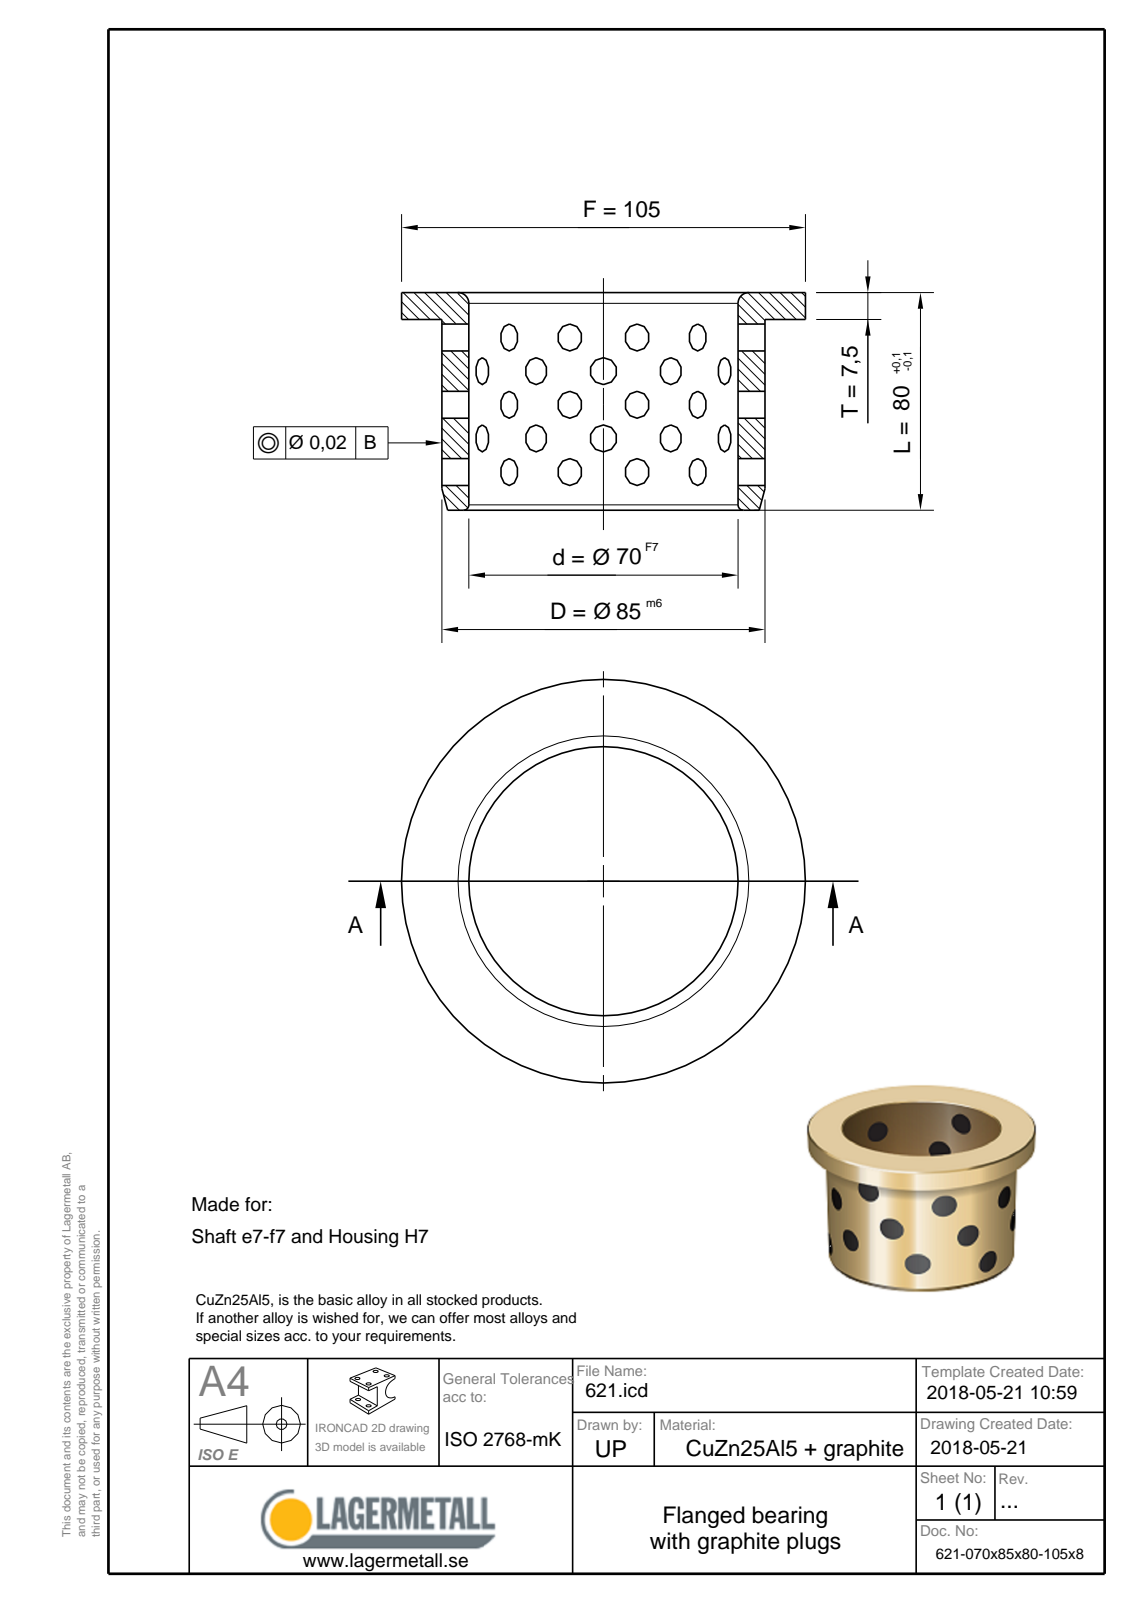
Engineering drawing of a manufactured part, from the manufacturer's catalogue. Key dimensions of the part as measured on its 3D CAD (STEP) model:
Part name (STEP PRODUCT): 621-070x85x80-105x8
STEP written by: Spatial InterOp 3D (CONFIG_CONTROL_DESIGN)
Units: millimetres
Bodies: 1 solid, 9 faces (3 planar, 3 cylindrical, 3 other)
Overall size (bounding box): 105 × 105 × 80
Volume: 167 597 mm³ · Surface area: 48 339 mm²
Round holes (diameter × count): ⌀70 ×1
Round bosses / shafts (diameter × count): ⌀105 ×1, ⌀85 ×1
Main face-to-face distances: 7.5, 72.5, 80
